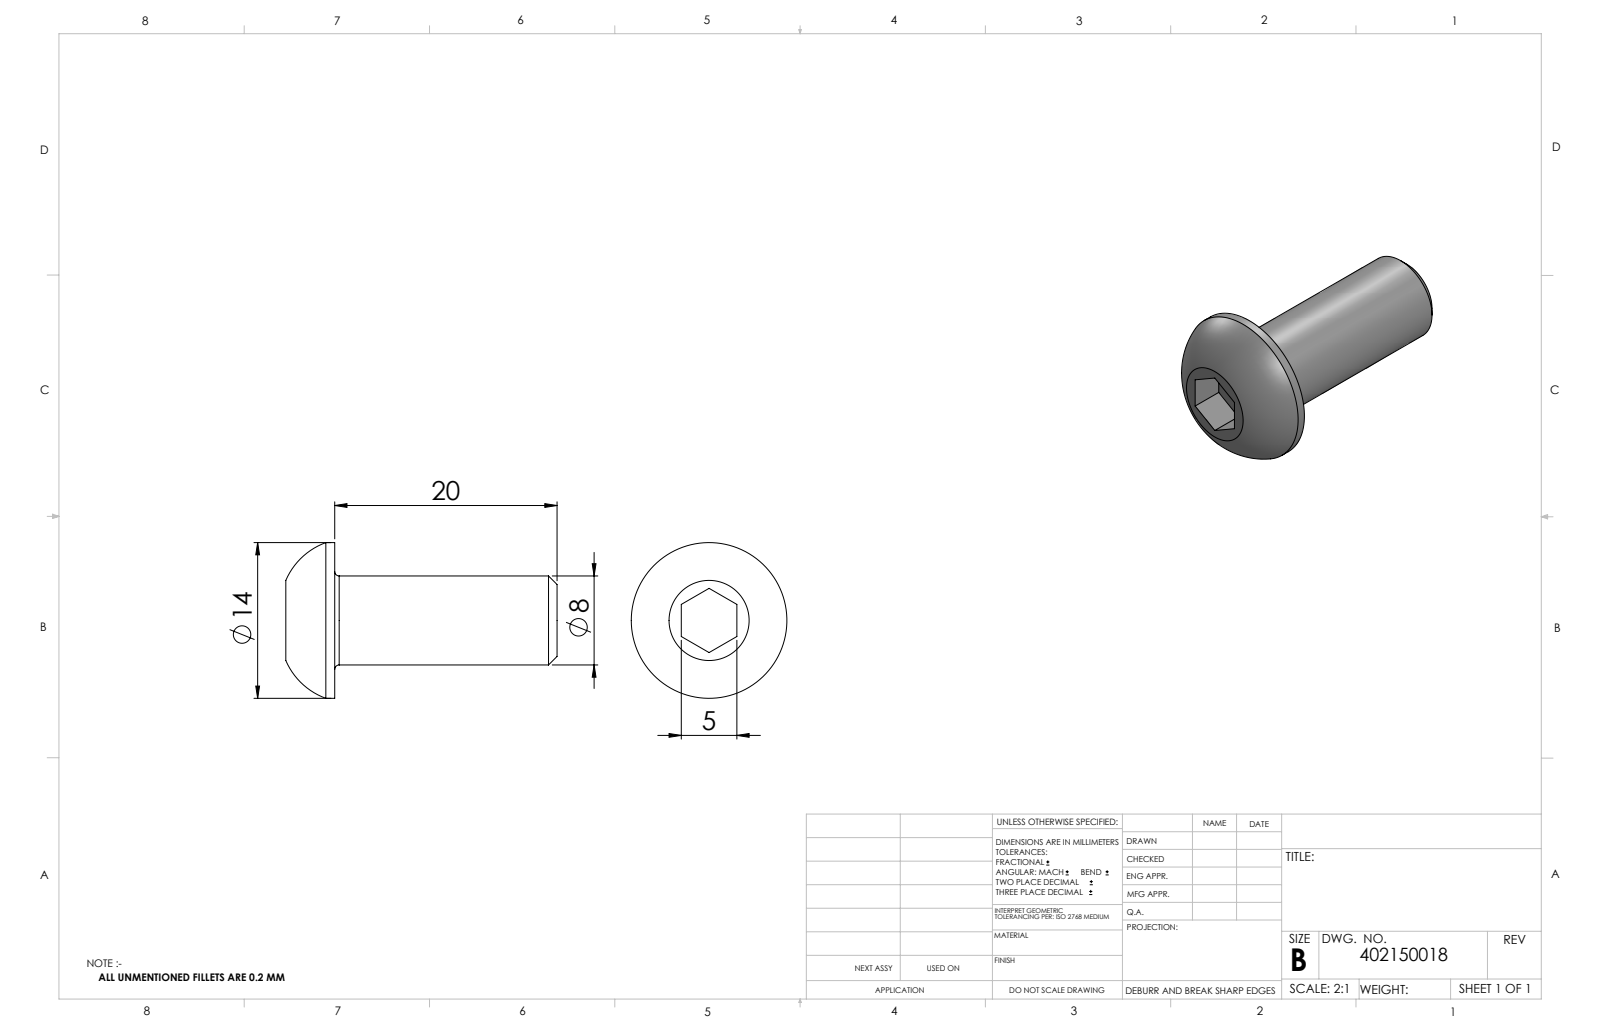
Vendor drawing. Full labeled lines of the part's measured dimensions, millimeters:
Part name (STEP PRODUCT): 402150018_c_1
STEP written by: SolidWorks 2014 (CONFIG_CONTROL_DESIGN)
Units: millimetres
Bodies: 1 solid, 20 faces (10 planar, 4 cylindrical, 6 other)
Overall size (bounding box): 24.4 × 14 × 14
Volume: 1 445 mm³ · Surface area: 945 mm²
Round bosses / shafts (diameter × count): ⌀14 ×1, ⌀8 ×1
Main face-to-face distances: 20, 5, 21.4, 1.4, 24.4, 4.4, 3
